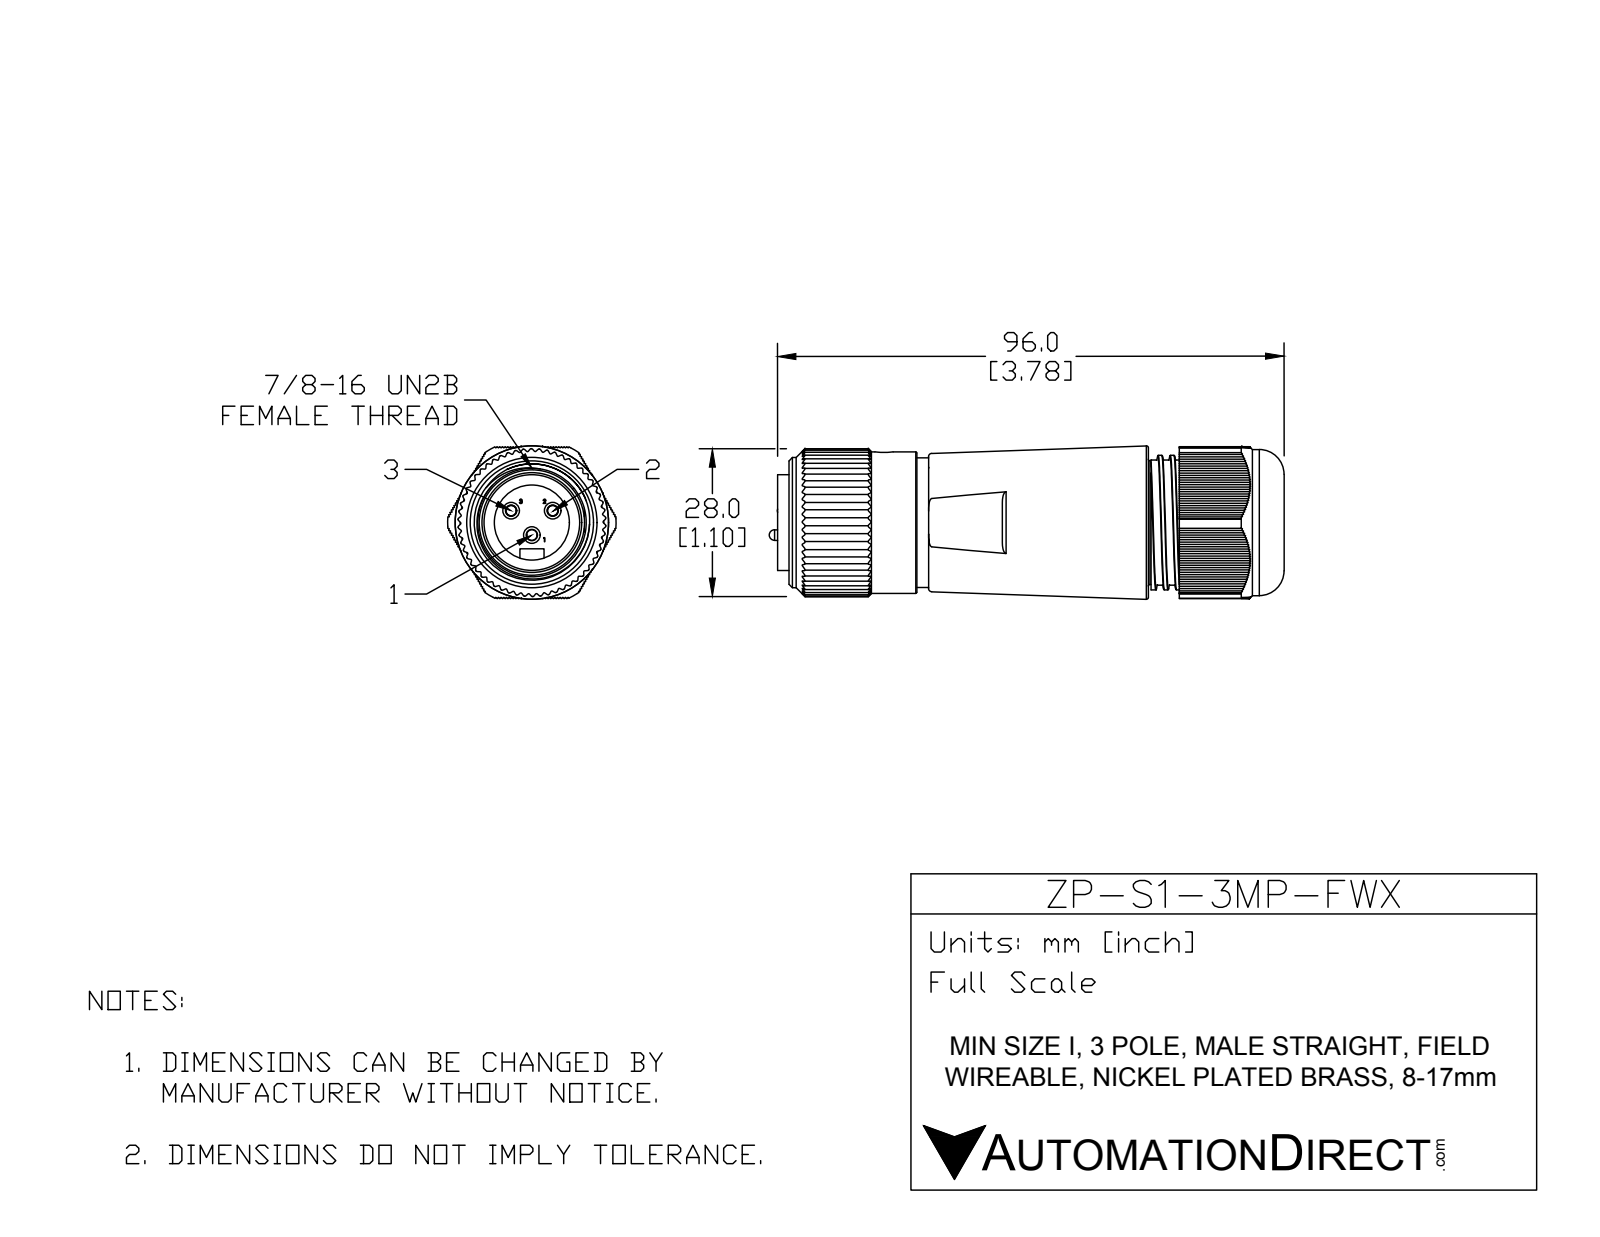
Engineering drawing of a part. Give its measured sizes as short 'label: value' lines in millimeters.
name: MIN-3MP-FWX
written by: SolidWorks 2015 (AUTOMOTIVE_DESIGN)
unit: mm
bodies: 1 solid, 1081 faces (669 planar, 339 cylindrical, 73 other)
size: 97.55 × 31.9 × 29.06
volume: 53 586 mm³; area: 15 911 mm²
holes: 1× ⌀3.5, 1× ⌀14.22, 1× ⌀17.27, 1× ⌀20.57, 1× ⌀24.13, 1× ⌀25.4
bosses: 3× ⌀3.15, 3× ⌀2, 1× ⌀27.69, 1× ⌀26.8, 1× ⌀25.5, 1× ⌀24.68, 1× ⌀24.56, 1× ⌀24
rounds: 116× R0.25, 58× R0.2, 1× R2.29, 1× R14, 1× R15.95
face distances: 0.36, 0.72, 18.94, 1.08, 18.92, 18.24, 1.44, 63.93, 5.84, 24.08
